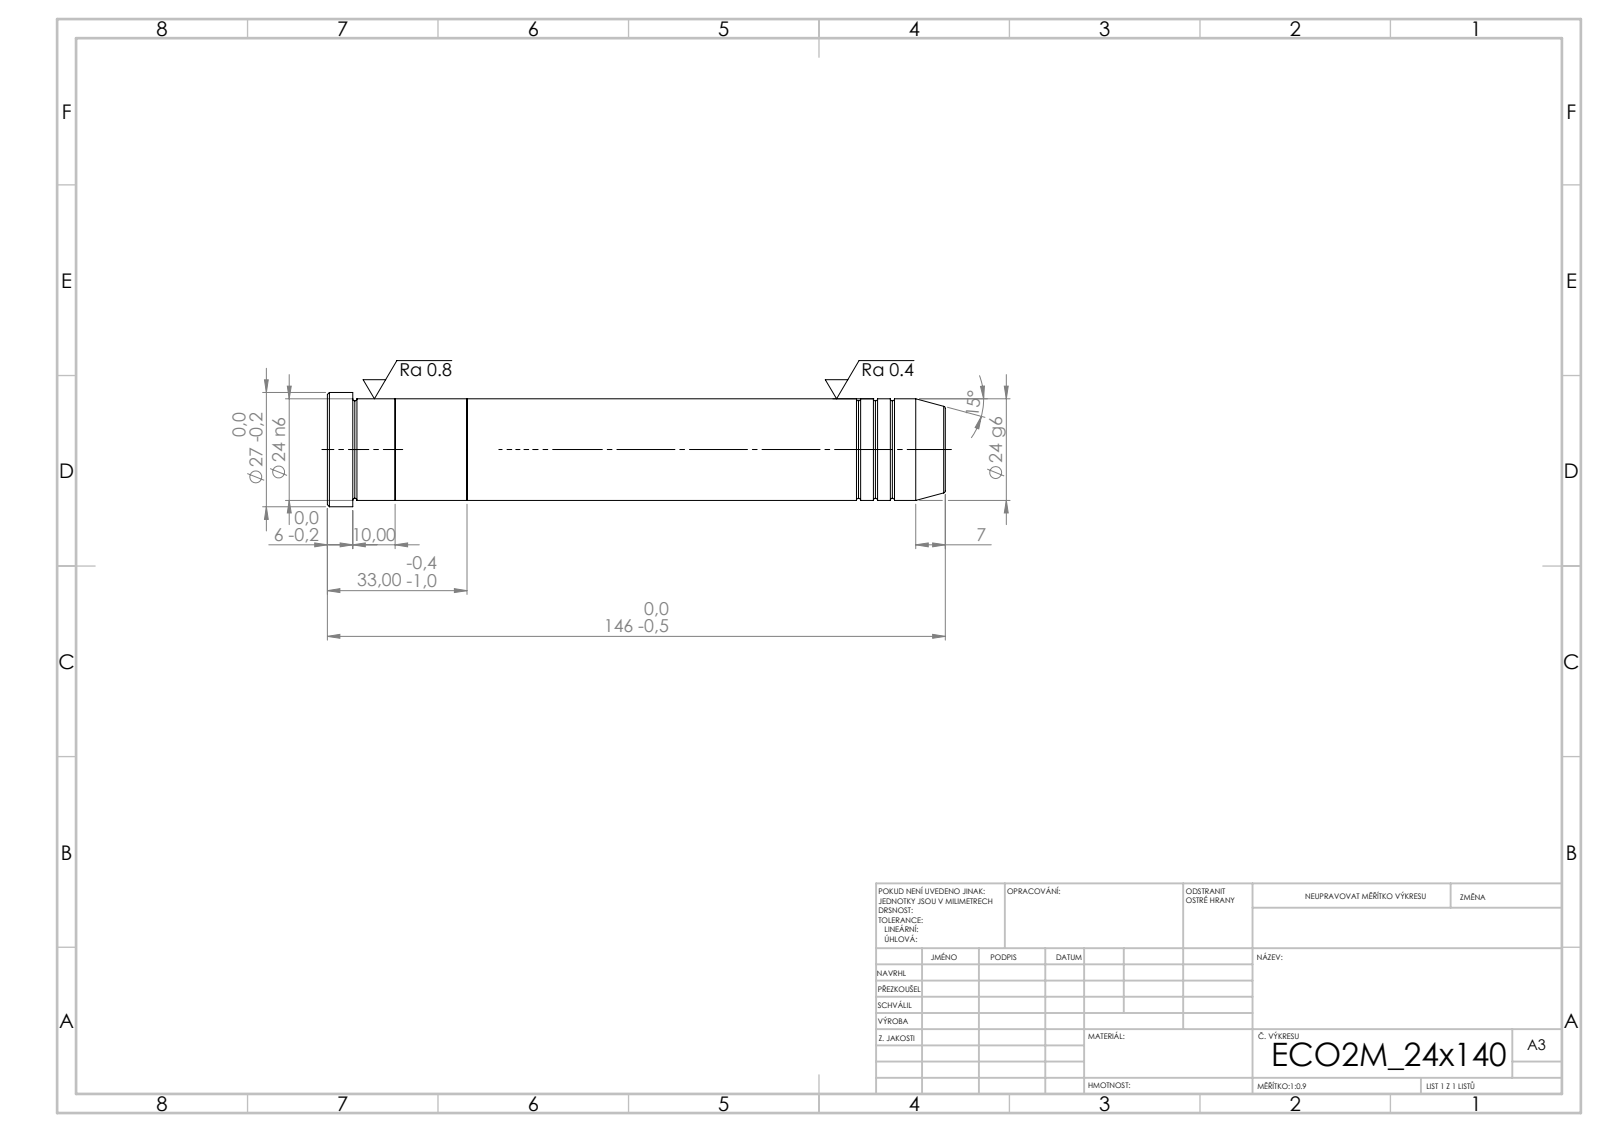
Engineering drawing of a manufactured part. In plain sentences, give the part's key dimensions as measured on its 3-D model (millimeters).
Its 3-D file was written by "SolidWorks 2019 (CONFIG_CONTROL_DESIGN)". It is 3 solids with 43 faces: 7 planar, 14 cylindrical and 22 other. Overall it measures 146 by 27 by 27 millimeters. Its volume is 66 172 cubic millimeters and its surface area 13 992 square millimeters. Round bosses or shafts: 1 of diameter 27, 1 of diameter 24. The main face-to-face distances are 17, 33, 16, 113, 130, 146, 140, 27, 10, 6.
